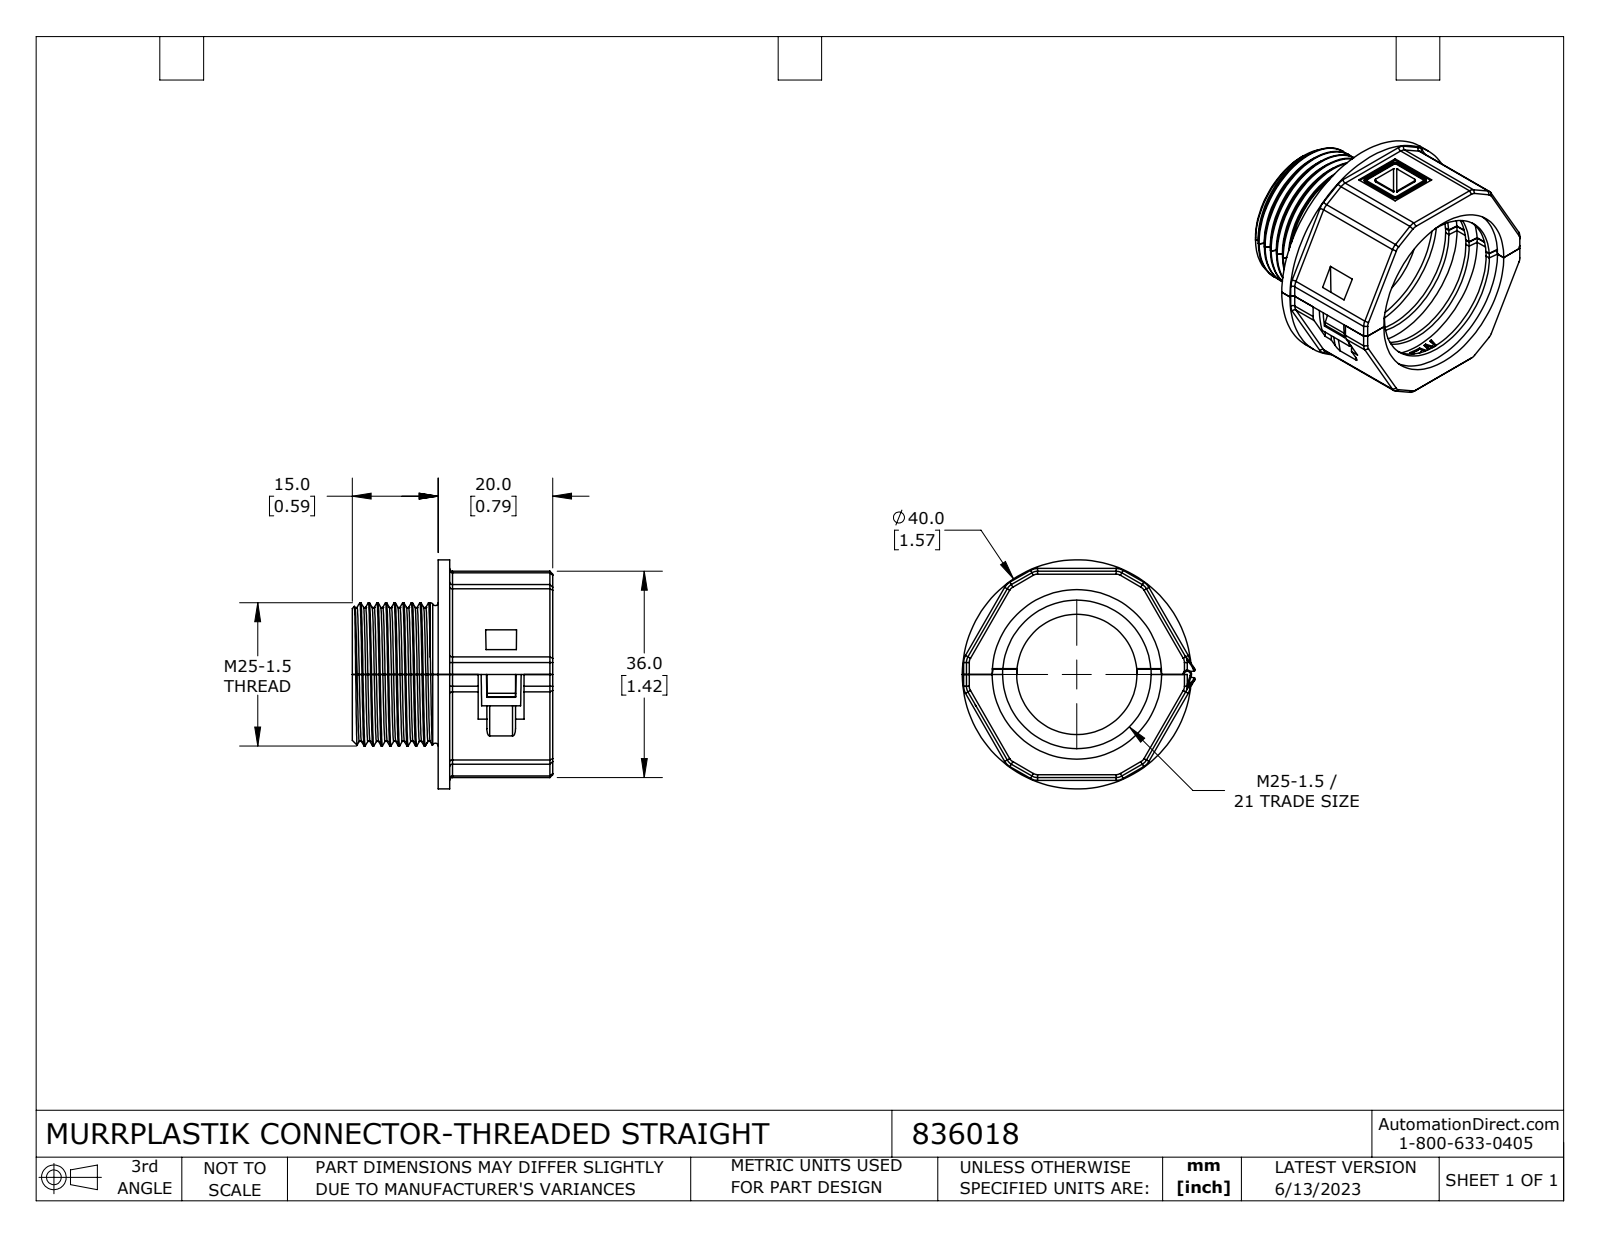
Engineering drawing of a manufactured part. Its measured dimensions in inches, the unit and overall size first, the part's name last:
Units: inches
Overall size (bounding box): 1.6 × 1.575 × 1.378
Round holes (diameter × count): ⌀0.059 ×1, ⌀0.197 ×1, ⌀0.827 ×1, ⌀1.02 ×1, ⌀1.165 ×1
Round bosses / shafts (diameter × count): ⌀1.575 ×1, ⌀0.984 ×1
Partial cylindrical surfaces — rounded edges, fillets, slot ends (radius × count): R0.008 ×32, R0.02 ×22, R0.079 ×13, R0.059 ×7, R0.013 ×4, R0.016 ×4, R0.025 ×4, R0.394 ×1
Main face-to-face distances: 0.709, 1.417, 0.669, 0.118, 0.787, 0.039, 1.518, 0.079, 0.591, 0.748
Hole centre spacings: 0.759
Volume: 0.698 in³ · Surface area: 16.42 in²
Bodies: 2 solids, 732 faces (345 planar, 170 cylindrical, 217 other)
Part name (STEP PRODUCT): 836018
STEP written by: SolidWorks 2021 (CONFIG_CONTROL_DESIGN)
